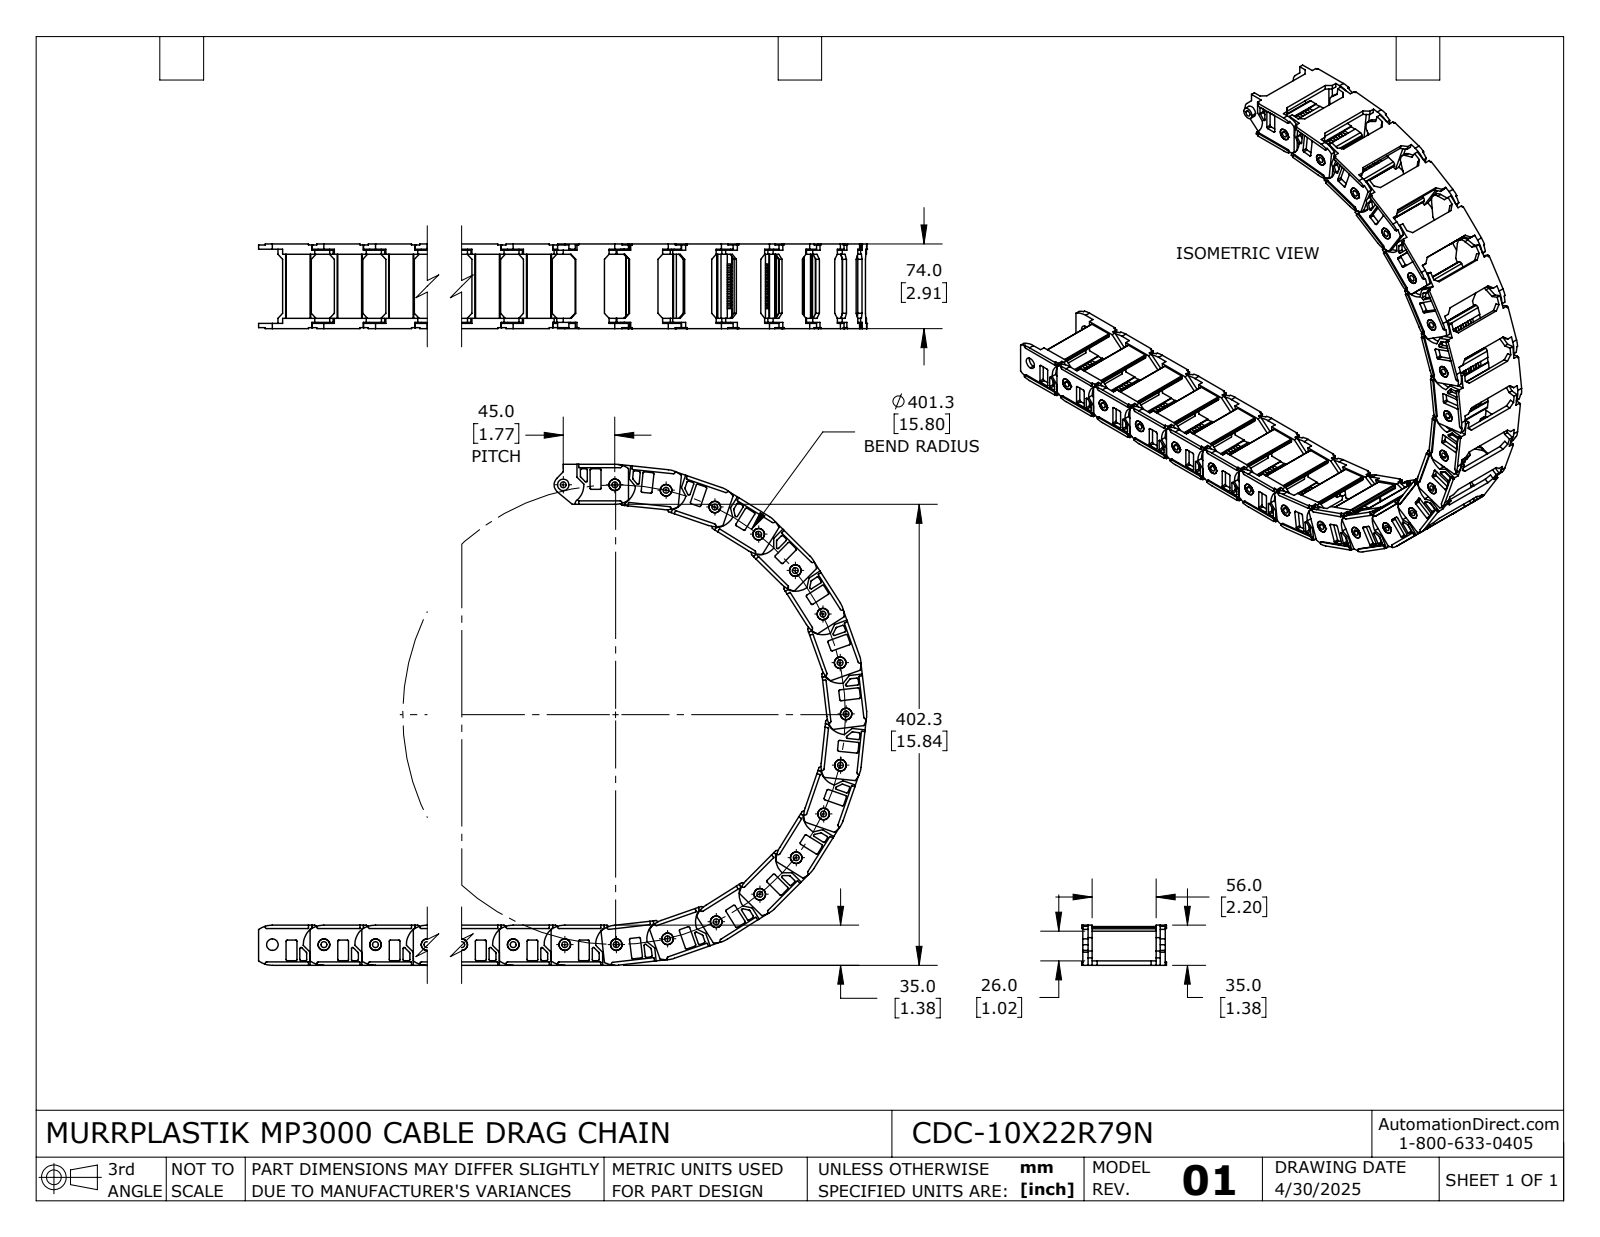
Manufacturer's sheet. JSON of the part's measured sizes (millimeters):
{"part_name": "CDC-10X22R79N", "step_written_by": "SolidWorks 2024 (AUTOMOTIVE_DESIGN)", "units": "millimeters", "bodies": {"solids": 22, "faces": 4224, "planar": 3124, "cylindrical": 1100, "other": 0}, "overall_size": [545.68, 437.29, 74], "volume_mm3": 657728, "surface_area_mm2": 397693, "round_holes": [[5.1, 22], [10.1, 22]], "round_bosses_or_shafts": [[10, 22]], "partial_cylinders_radius": [[1, 176], [0.5, 88], [1.5, 44], [2, 44], [21, 44], [2.8, 22], [8, 22], [18, 22]], "face_to_face_distances": [64, 8, 4, 3.7, 68.3, 4.3, 60.3, 3.5, 56, 0.8], "hole_center_spacings": [174.43, 45, 45.02, 89.46, 132.82, 174.47, 213.87, 132.78]}
